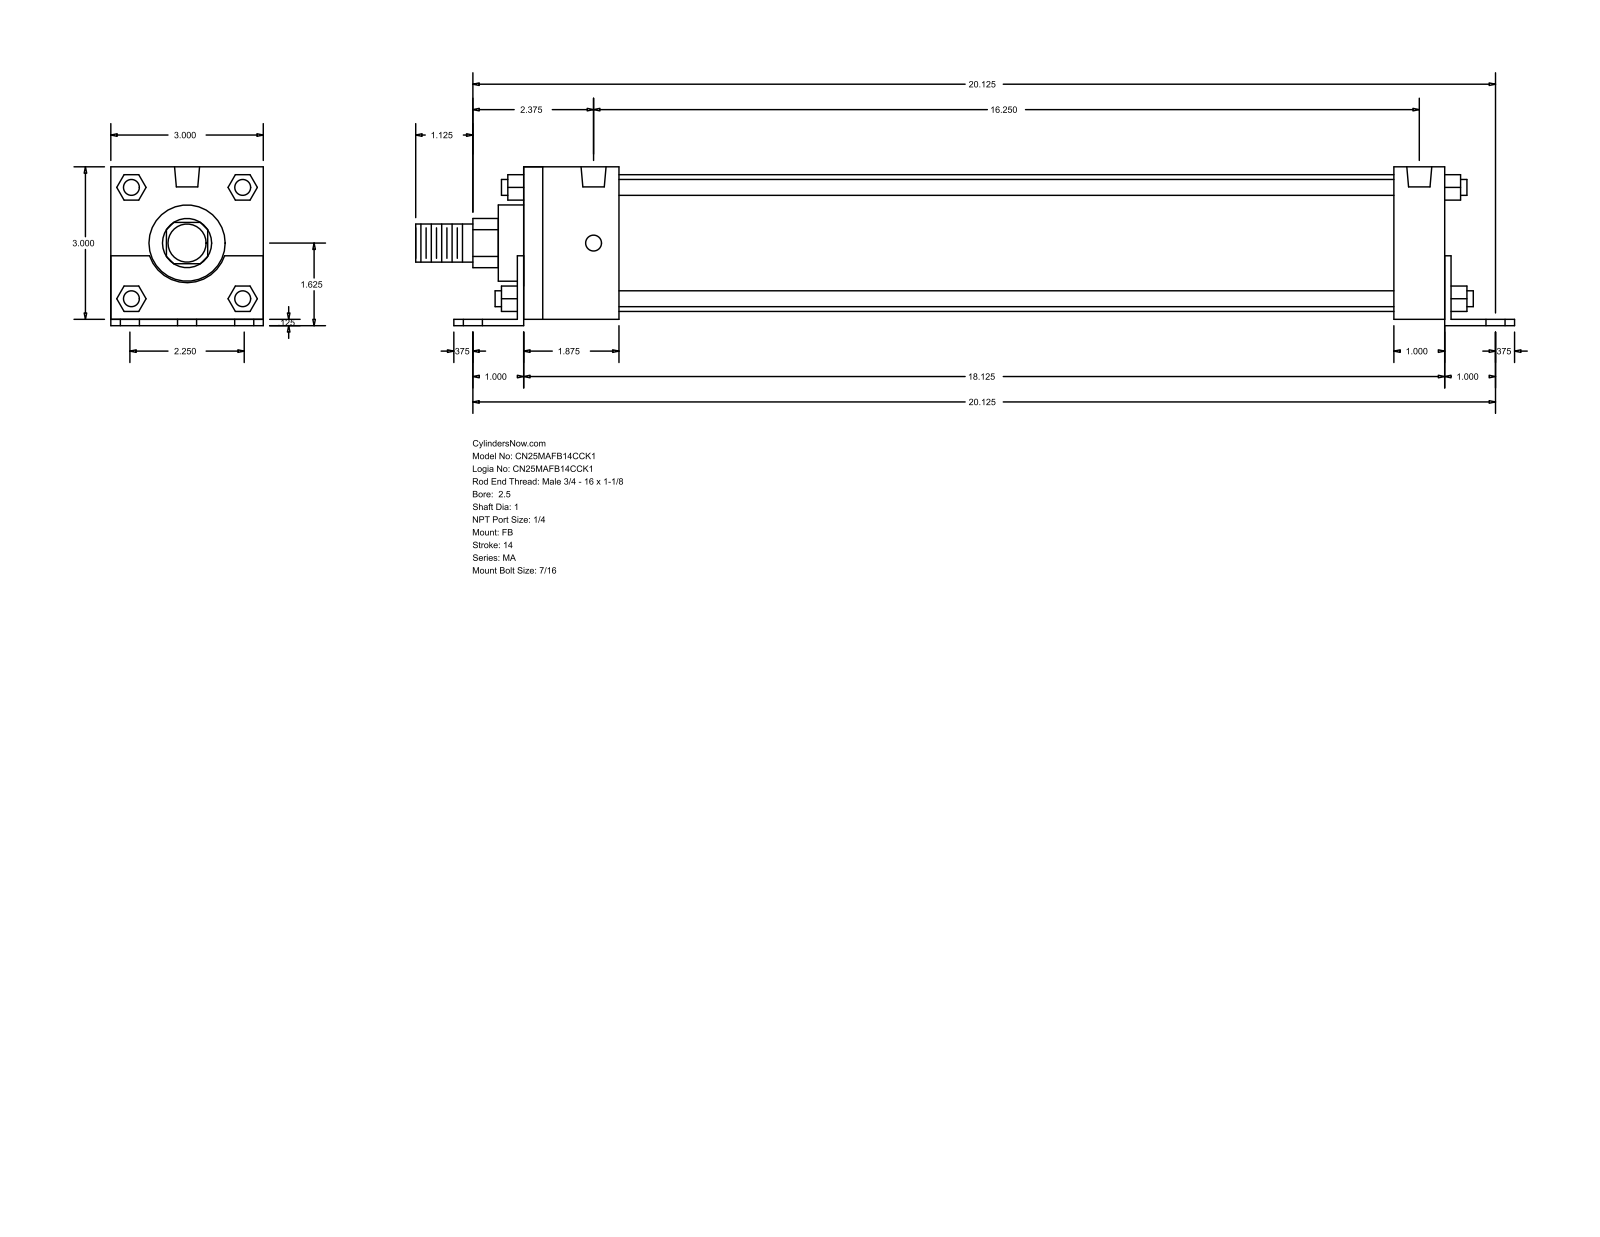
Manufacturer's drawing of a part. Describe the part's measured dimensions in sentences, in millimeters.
The part is named "MA_FB__0250_1". Its 3-D file was written by "GSSL Pune (CONFIG_CONTROL_DESIGN)". It is 0 solids with 140 faces: 105 planar, 35 cylindrical and 0 other. Overall it measures 549.27 by 79.38 by 76.2 millimeters. Round holes: 6 of diameter 11.11, 4 of diameter 7.94, 2 of diameter 12.49. Round bosses or shafts: 4 of diameter 7.94, 1 of diameter 68.33, 1 of diameter 38.1, 1 of diameter 25.4, 1 of diameter 19.05. Partial cylindrical surfaces (rounded edges, fillets, slot ends): 1 of radius 12.29, 1 of radius 19.81. The main face-to-face distances are 76.2, 3.17, 79.37, 460.37, 3.18, 12.7, 463.55, 28.57, 50.8, 47.63. The hole center spacings are 28.57, 511.98, 511.18, 47.63, 57.14, 66.75, 412.74, 451.75.
